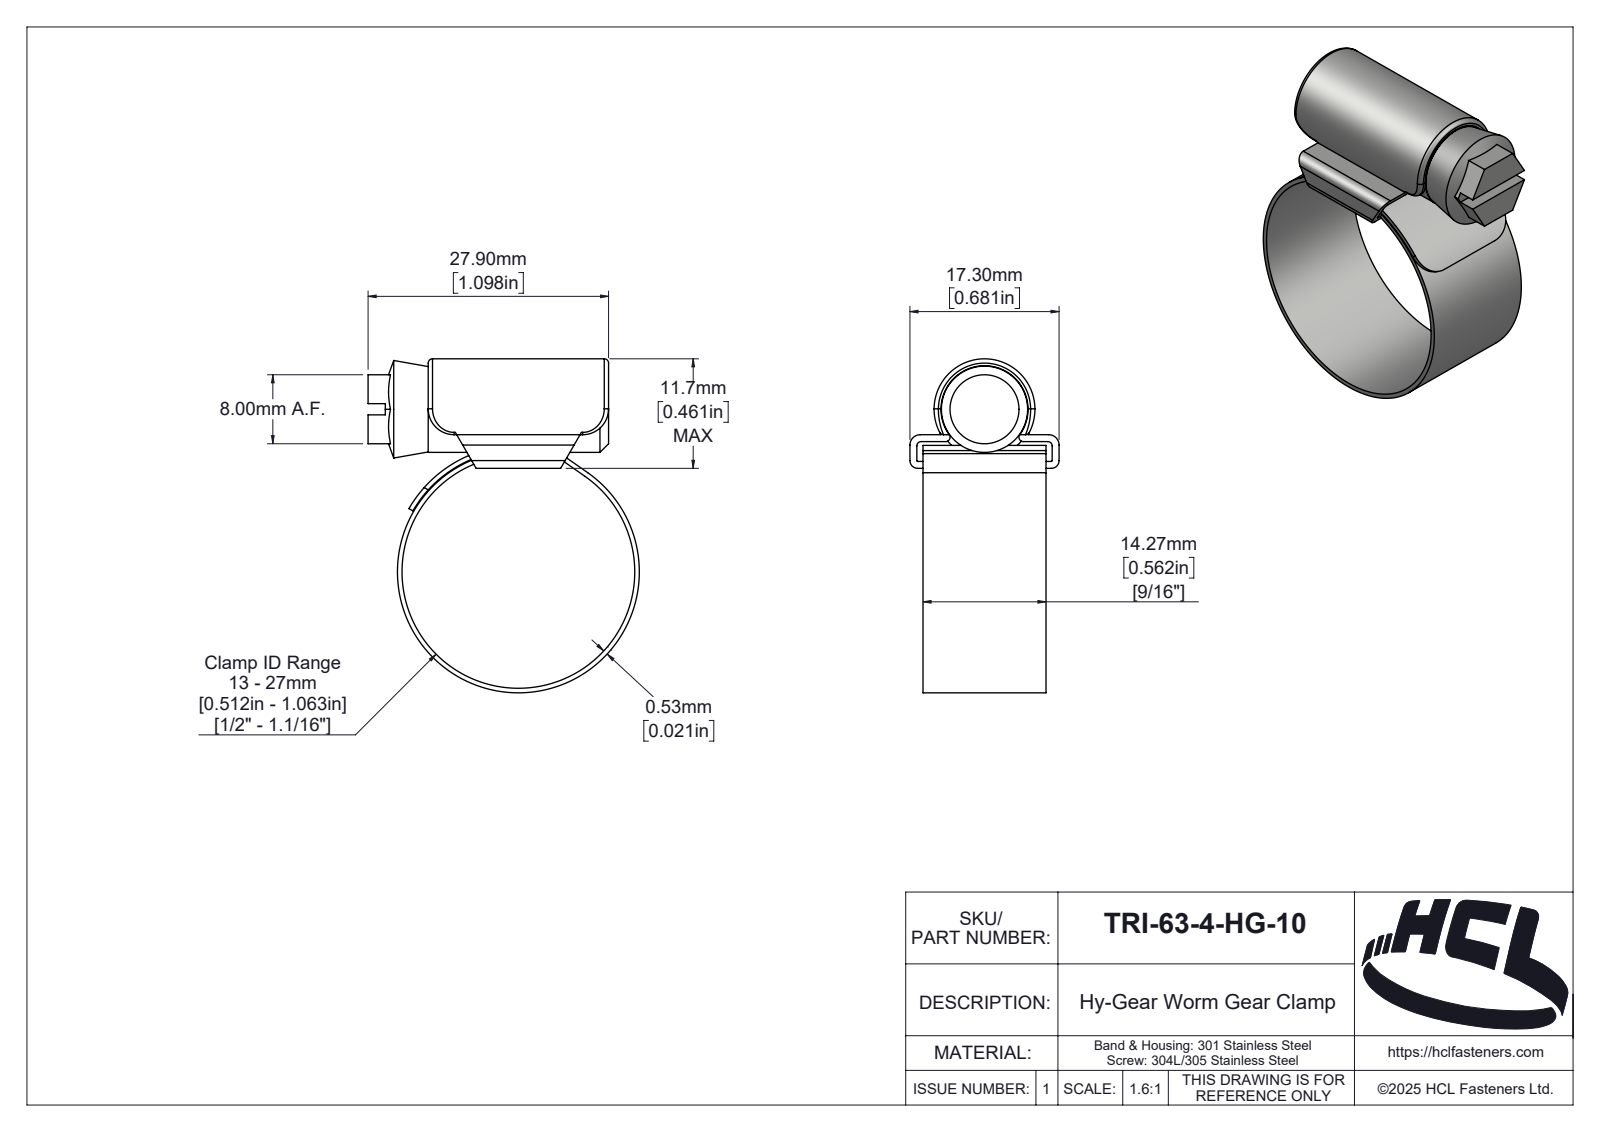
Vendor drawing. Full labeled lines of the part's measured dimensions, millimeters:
Part name (STEP PRODUCT): TRI-50-0-HG-10
STEP written by: SolidWorks 2025 (AUTOMOTIVE_DESIGN)
Units: millimetres
Bodies: 3 solids, 189 faces (39 planar, 89 cylindrical, 61 other)
Overall size (bounding box): 38.73 × 31.47 × 17.3
Volume: 3 561 mm³ · Surface area: 5 815 mm²
Round holes (diameter × count): ⌀27 ×1
Round bosses / shafts (diameter × count): ⌀28.06 ×1, ⌀10 ×1
Partial cylindrical surfaces — rounded edges, fillets, slot ends (radius × count): R0.5 ×6, R3 ×4, R0.1 ×2, R0.9 ×2, R1.2 ×2, R0.46 ×1, R1.89 ×1, R2 ×1
Main face-to-face distances: 0.8, 3.1, 2.3, 3.9, 0.53, 14.26, 27.9, 1.52, 15.78, 16.5
